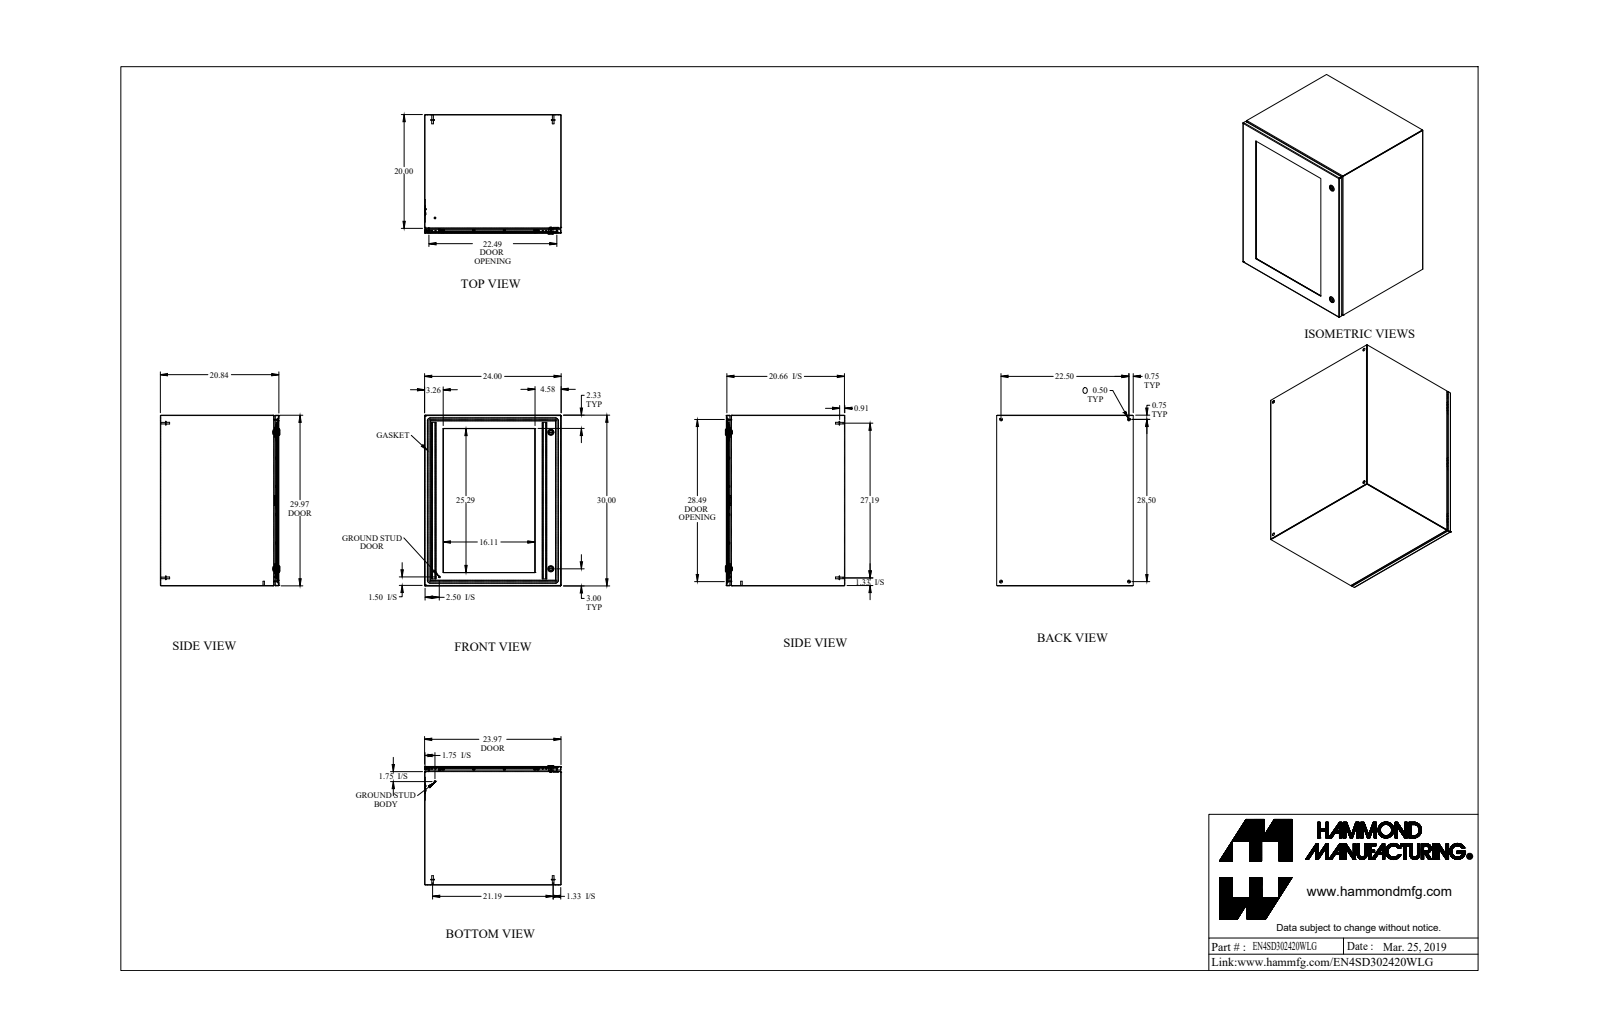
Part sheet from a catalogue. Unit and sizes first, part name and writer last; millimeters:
Units: millimetres
Overall size (bounding box): 762 × 609.6 × 533.3
Round holes (diameter × count): ⌀3.3 ×20, ⌀6.4 ×20, ⌀12.7 ×4, ⌀5.9 ×2, ⌀15.9 ×2, ⌀19.9 ×2, ⌀4.4 ×1, ⌀6.1 ×1, ⌀6.1 ×1
Round bosses / shafts (diameter × count): ⌀5.7 ×21, ⌀9.3 ×20, ⌀4.2 ×20, ⌀15.9 ×4, ⌀8 ×4, ⌀6.9 ×4, ⌀27.9 ×2, ⌀13.3 ×2
Partial cylindrical surfaces — rounded edges, fillets, slot ends (radius × count): R0.9 ×14, R2.7 ×14, R1.1 ×12, R2.1 ×12, R3.2 ×12, R7.9 ×12, R2.5 ×8, R0.2 ×6
Main face-to-face distances: 1.8, 607.8, 527.4, 760.2, 525.6, 605.9, 609.6, 519.3, 6.4, 521.1
Hole centre spacings: 252.7, 503.5, 126.4, 136.4, 422.8, 435.5, 453.4, 682.6
Volume: 6 130 000 mm³ · Surface area: 5 430 000 mm²
Bodies: 82 solids, 1605 faces (810 planar, 499 cylindrical, 296 other)
Part name (STEP PRODUCT): EN4SD302420WLG
STEP written by: SolidWorks 2019 (AUTOMOTIVE_DESIGN)
